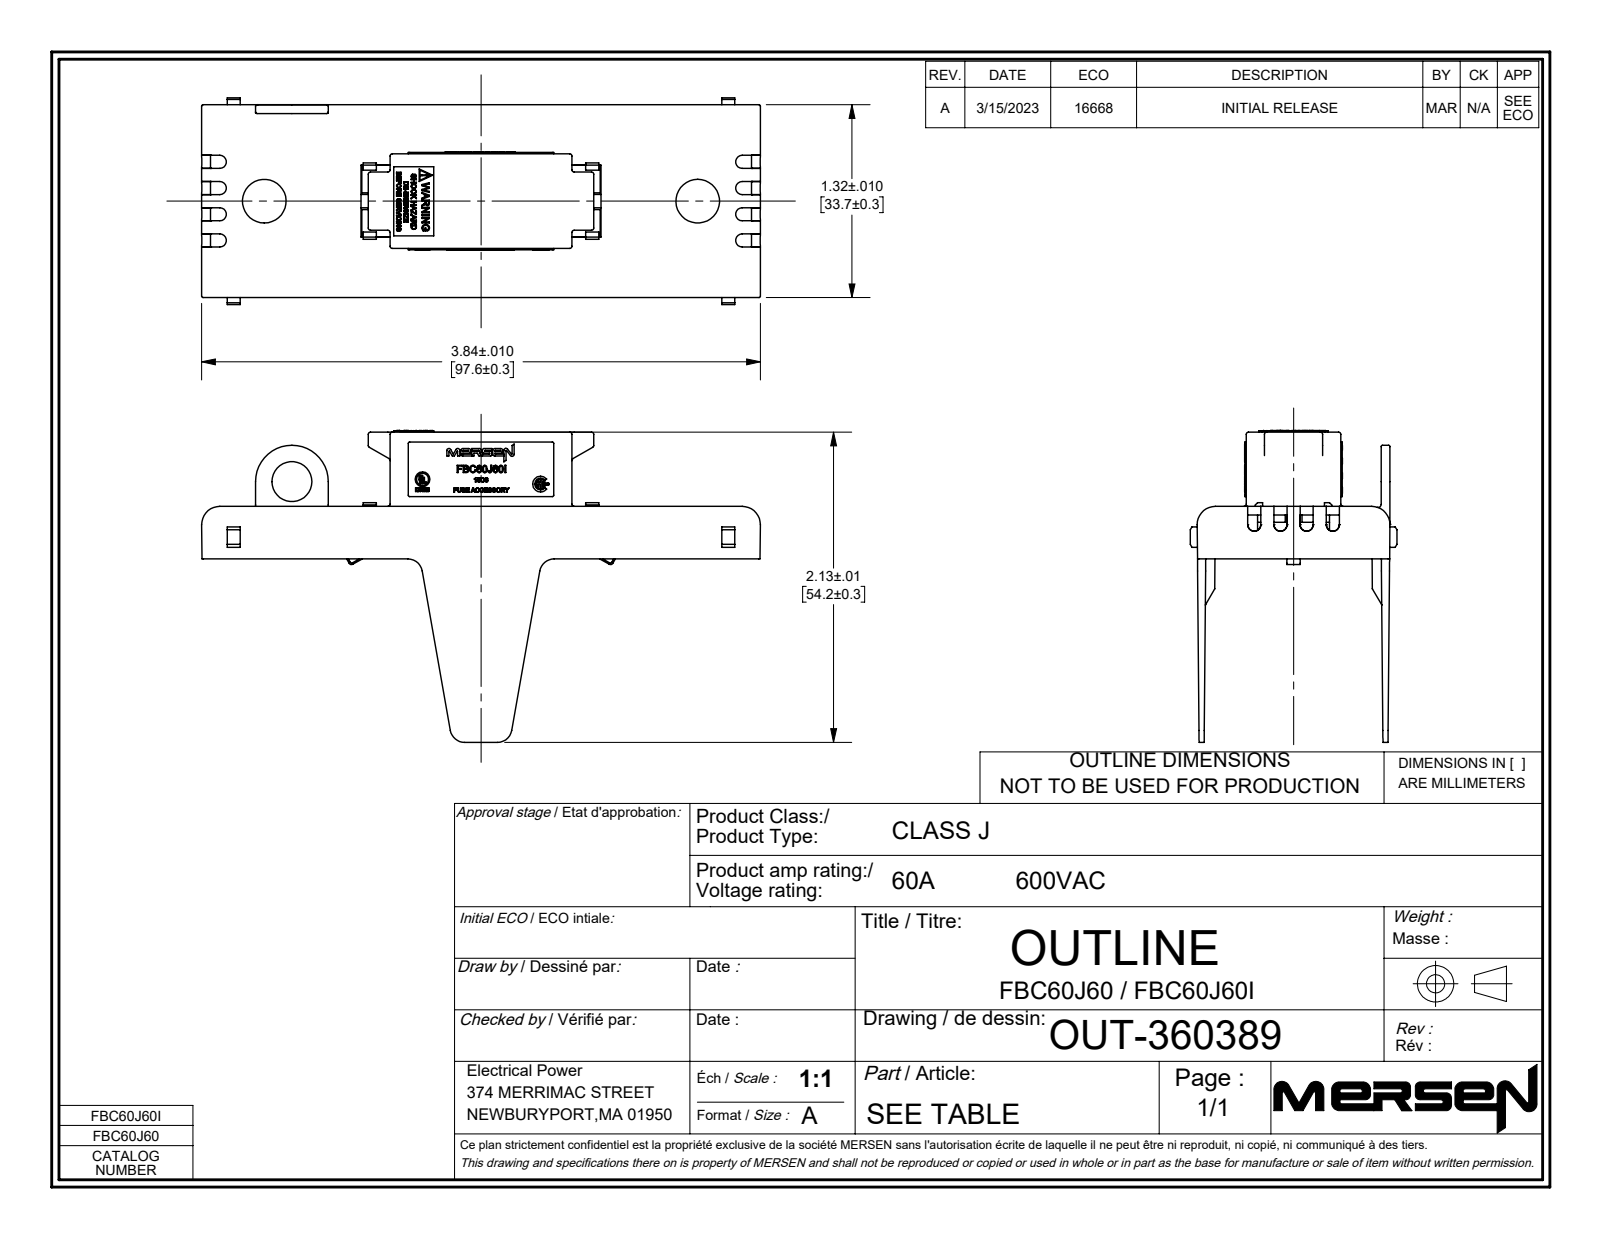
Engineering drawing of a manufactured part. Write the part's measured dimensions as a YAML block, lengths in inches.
part_name: "OUT-360389; 1203655; 330838; 1203190 (+1 more)"
step_written_by: "SolidWorks 2021 (AUTOMOTIVE_DESIGN)"
units: inches
bodies: {solids: 4, faces: 2278, planar: 1225, cylindrical: 167, other: 886}
overall_size: [3.841, 2.143, 1.421]
volume: 0.674
surface_area: 24.91
round_holes:
  - {diameter: 0.3, count: 2}
  - {diameter: 0.275, count: 1}
partial_cylinders:
  - {radius: 0.01, count: 49}
  - {radius: 0.015, count: 32}
  - {radius: 0.045, count: 16}
  - {radius: 0.125, count: 6}
  - {radius: 0.065, count: 4}
  - {radius: 0.1, count: 4}
  - {radius: 0.02, count: 1}
  - {radius: 0.25, count: 1}
face_to_face_distances: [1.264, 0.06, 0.57, 0.51, 0.65, 0.087, 0.583, 0.078, 0.572, 0.573]
hole_center_spacings: [2.98]
